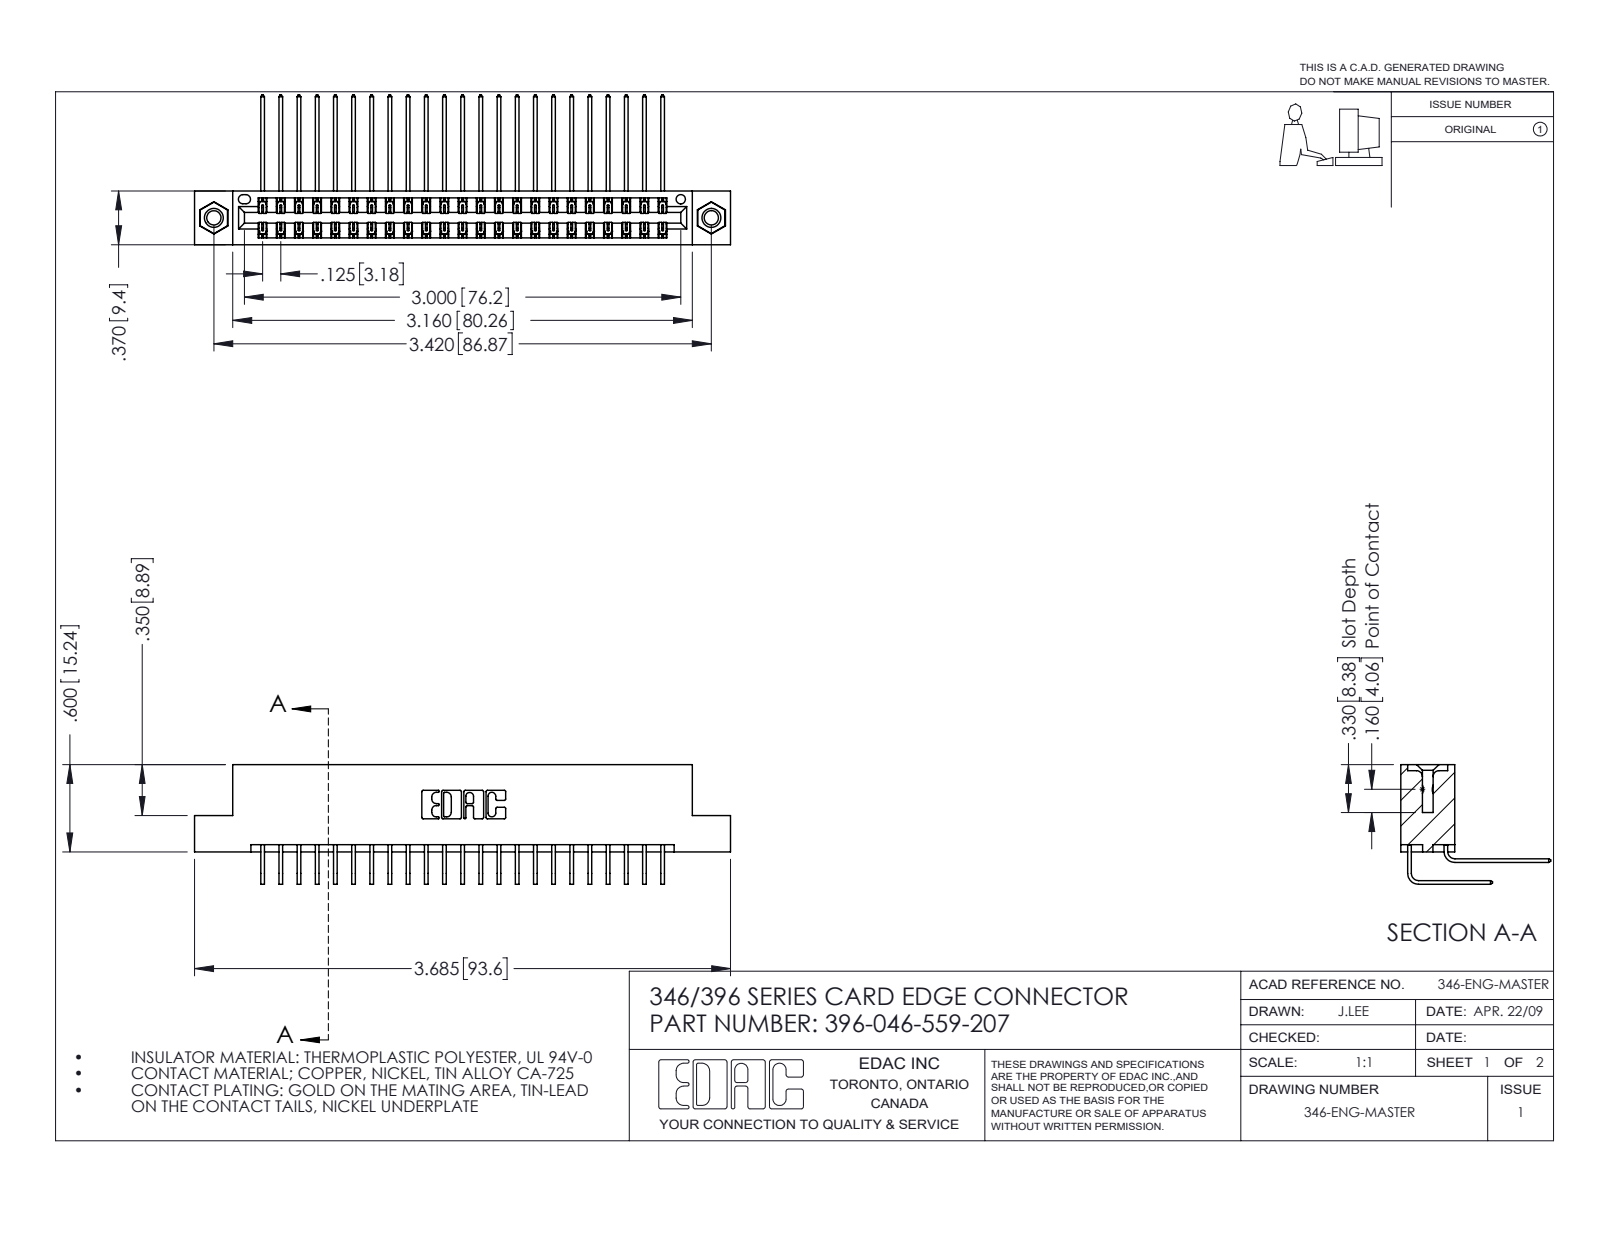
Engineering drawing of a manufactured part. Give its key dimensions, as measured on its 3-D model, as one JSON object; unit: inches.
{"part_name": "396-046-559-207; 346 Part_Flush Mounting Lugs - 0.156 Dia-TI; 345-292-001_559 Tail - 2; 345-250-001_345-250-005-103 (+1 more)", "step_written_by": "SolidWorks 2016 (CONFIG_CONTROL_DESIGN)", "units": "inches", "bodies": {"solids": 49, "faces": 2666, "planar": 1810, "cylindrical": 840, "other": 16}, "overall_size": [3.685, 1.03, 0.823], "volume_in3": 0.563, "surface_area_in2": 21.23, "round_holes": [[0.098, 2], [0.125, 2], [0.156, 2], [0.064, 1]], "round_bosses_or_shafts": [[0.155, 2]], "partial_cylinders_radius": [[0.006, 69], [0.01, 22], [0.007, 6], [0.031, 6], [0.026, 3], [0.014, 2], [0.022, 2], [0.024, 2]], "face_to_face_distances": [0.048, 0.322, 0.25, 0.025, 0.37, 0.072, 0.298, 0.275, 0.148, 0.222], "hole_center_spacings": [0.246, 3.212, 3.42]}
